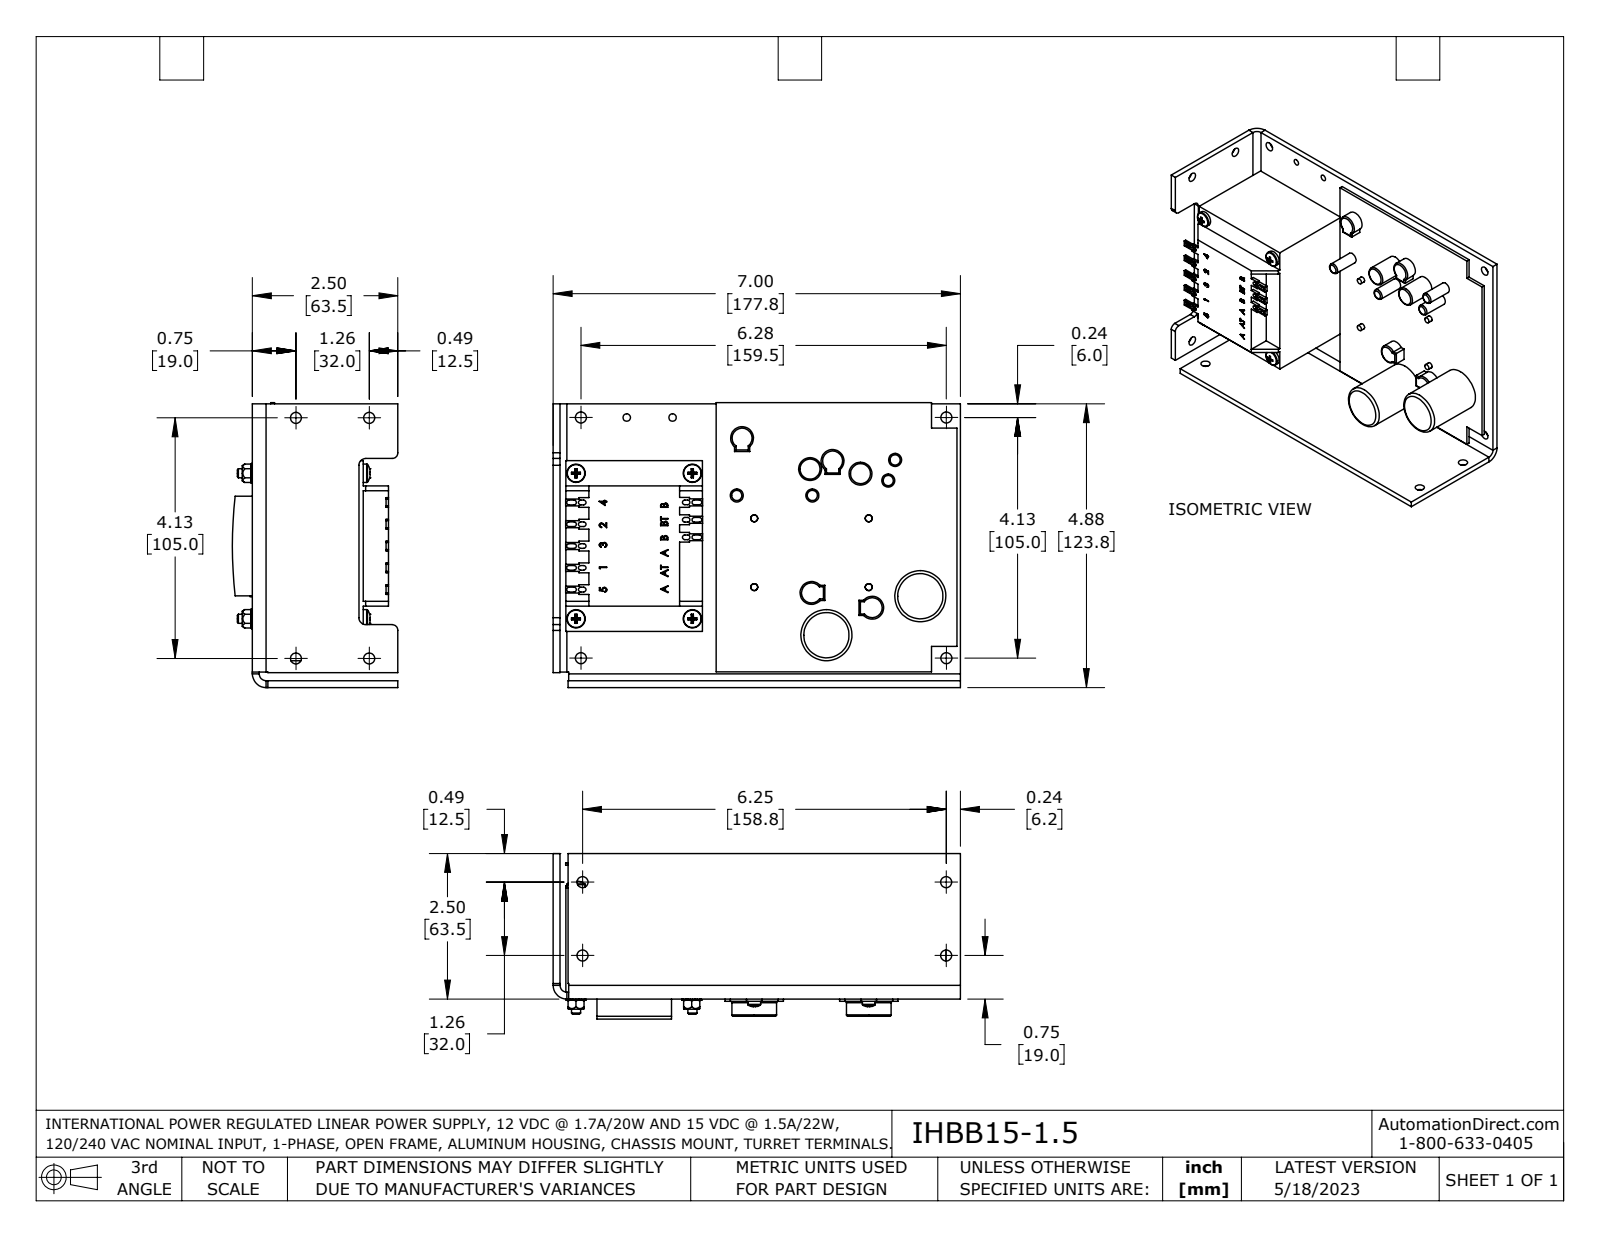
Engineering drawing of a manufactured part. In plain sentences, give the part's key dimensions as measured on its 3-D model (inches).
The part is named "IHBB15-1.5". Its 3-D file was written by "SolidWorks 2021 (AUTOMOTIVE_DESIGN)". It is 33 solids with 979 faces: 611 planar, 241 cylindrical and 127 other. Overall it measures 7 by 4.895 by 2.844 inches. Its volume is 24.71 cubic inches and its surface area 226.4 square inches. Round holes: 12 of diameter 0.189, 6 of diameter 0.13, 4 of diameter 0.115, 4 of diameter 0.12, 4 of diameter 0.138, 4 of diameter 0.157, 4 of diameter 0.169, 2 of diameter 0.128. Round bosses or shafts: 4 of diameter 0.315, 4 of diameter 0.25, 4 of diameter 0.225, 4 of diameter 0.22, 4 of diameter 0.118, 2 of diameter 0.878, 2 of diameter 0.768, 2 of diameter 0.394. Partial cylindrical surfaces (rounded edges, fillets, slot ends): 32 of radius 0.04, 12 of radius 0.025, 4 of radius 0.118, 4 of radius 0.126, 4 of radius 0.162, 4 of radius 0.167, 4 of radius 0.197, 2 of radius 0.1. The main face-to-face distances are 0.118, 0.262, 0.38, 0.065, 0.197, 0.315, 0.22, 0.102, 2.346, 2.449. The hole center spacings are 2.5, 1.26, 4.134, 0.787, 1.181, 1.969, 1.988, 2.
